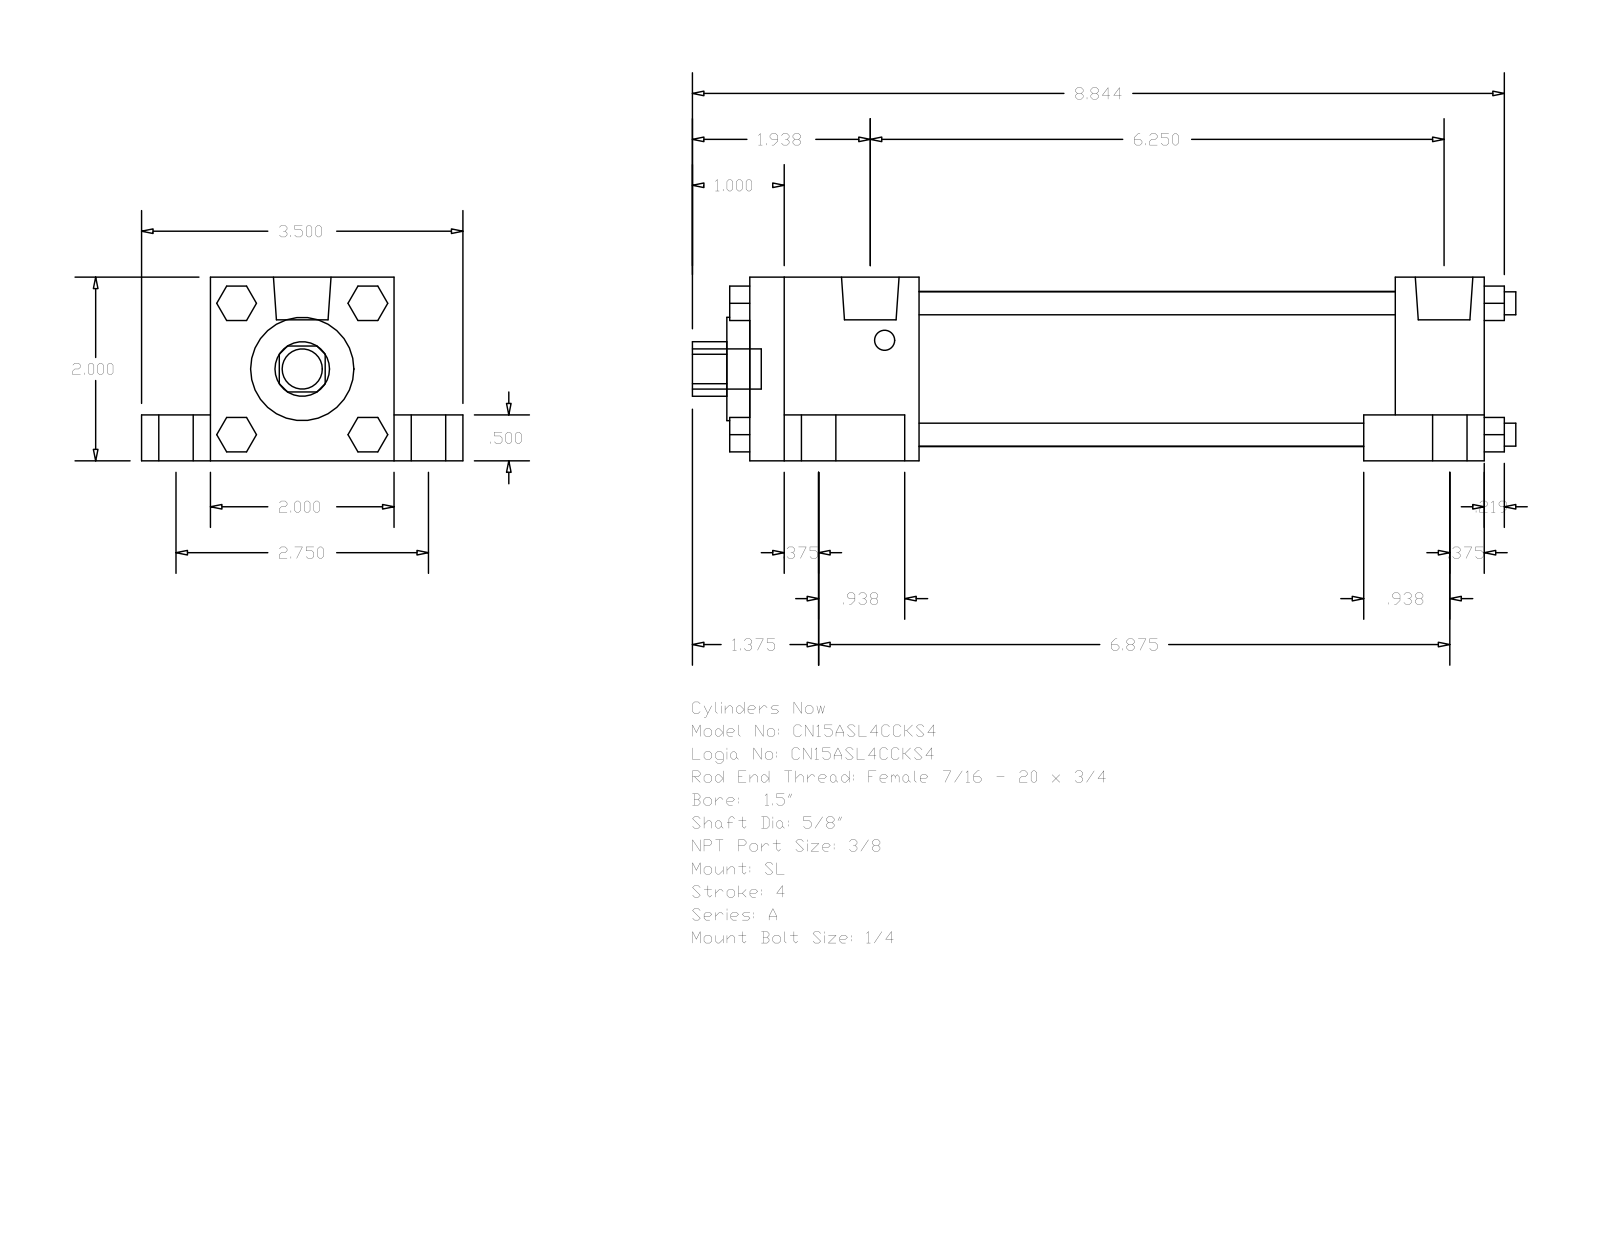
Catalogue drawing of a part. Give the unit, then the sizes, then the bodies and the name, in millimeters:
Units: millimetres
Overall size (bounding box): 227.81 × 88.9 × 50.8
Round holes (diameter × count): ⌀15.88 ×1, ⌀28.57 ×1, ⌀42.93 ×1
Round bosses / shafts (diameter × count): ⌀15.88 ×4, ⌀9.53 ×4, ⌀6.35 ×4, ⌀5.56 ×4, ⌀15.93 ×2, ⌀11.11 ×1
Partial cylindrical surfaces — rounded edges, fillets, slot ends (radius × count): R7.54 ×1
Main face-to-face distances: 50.8, 19.05, 12.7, 38.1, 69.85, 203.19, 9.52, 178.59, 24.6, 46.83
Bodies: 0 solids, 148 faces (112 planar, 36 cylindrical, 0 other)
Part name (STEP PRODUCT): A_SL__0150_0.625
STEP written by: GSSL Pune (CONFIG_CONTROL_DESIGN)
